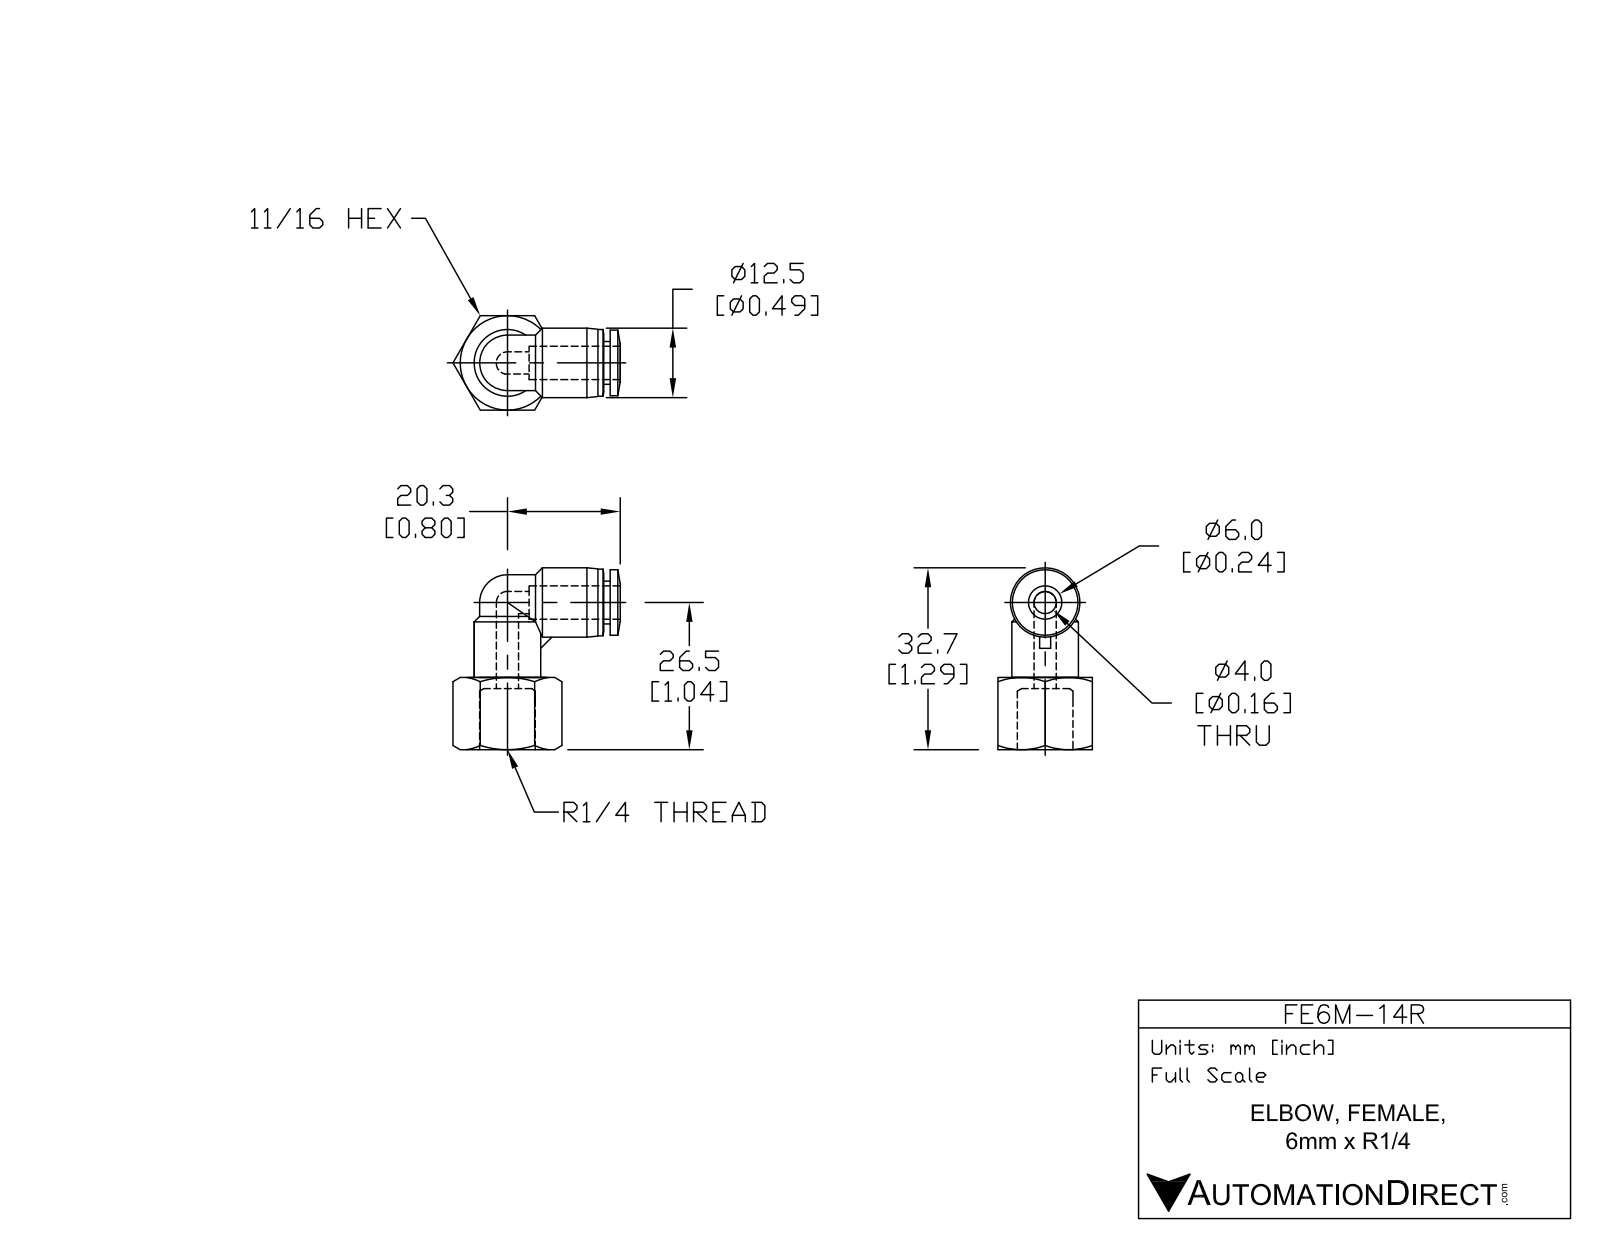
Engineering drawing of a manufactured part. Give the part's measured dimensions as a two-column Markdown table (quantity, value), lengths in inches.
| quantity | value |
| --- | --- |
| part name | FE6M-14R |
| STEP written by | SolidWorks 2015 (AUTOMOTIVE_DESIGN) |
| units | inches |
| bodies | 1 solid, 67 faces (17 planar, 19 cylindrical, 31 other) |
| overall size | 1.289 × 1.186 × 0.669 |
| volume | 0.277 in³ |
| surface area | 5.47 in² |
| round holes (diameter × count) | 0.157 × 2, 0.248 × 1 |
| round bosses / shafts (diameter × count) | 0.472 × 2, 0.492 × 1, 0.465 × 1, 0.303 × 1 |
| partial cylindrical surfaces (radius × count) | 0.197 × 2 |
| main face-to-face distances | 0.669, 0.079, 0.433, 0.512, 0.045, 0.53, 0.575, 0.295, 0.374, 0.646 |
